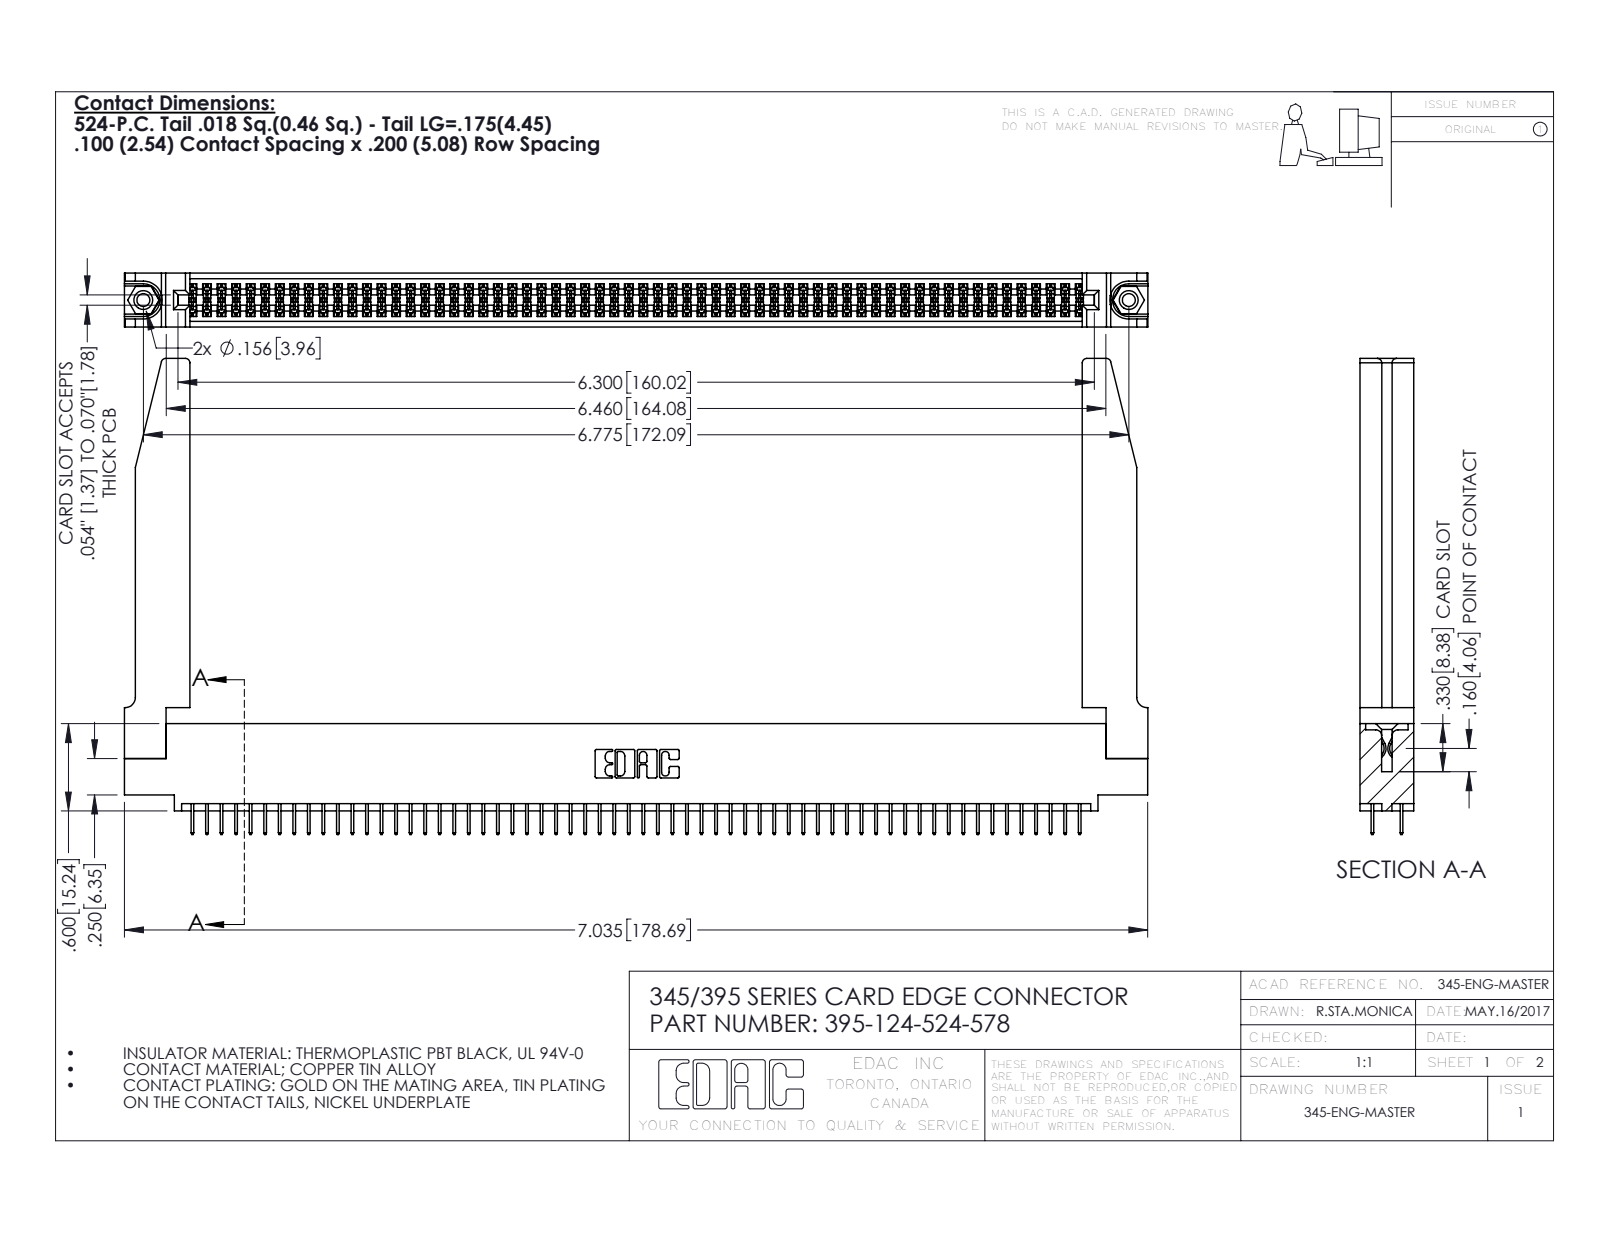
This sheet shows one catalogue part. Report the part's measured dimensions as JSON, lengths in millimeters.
{"part_name": "345-292-001_345-293-124; 345-250-001_345-250-001-102; 345 Part_0.110 Offset - 0.156 Dia-TH; 345-220-078_345-220-078 (+1 more)", "step_written_by": "SolidWorks 2016 (CONFIG_CONTROL_DESIGN)", "units": "millimeters", "bodies": {"solids": 129, "faces": 7060, "planar": 5062, "cylindrical": 1946, "other": 52}, "overall_size": [178.7, 83.1, 9.4], "volume_mm3": 25060, "surface_area_mm2": 32370, "round_holes": [[2.3, 2], [3.2, 2], [4, 2], [1.6, 1]], "round_bosses_or_shafts": [[3.9, 2]], "partial_cylinders_radius": [[0.2, 186], [0.3, 22], [0.8, 8], [0.2, 6], [0.8, 6], [0.7, 3], [0.4, 2], [0.5, 2]], "face_to_face_distances": [1.8, 9.4, 7.6, 5.1, 2.5, 6.9, 0.6, 5.7, 1.8, 4.4], "hole_center_spacings": [6.9, 166.1, 172.1]}
